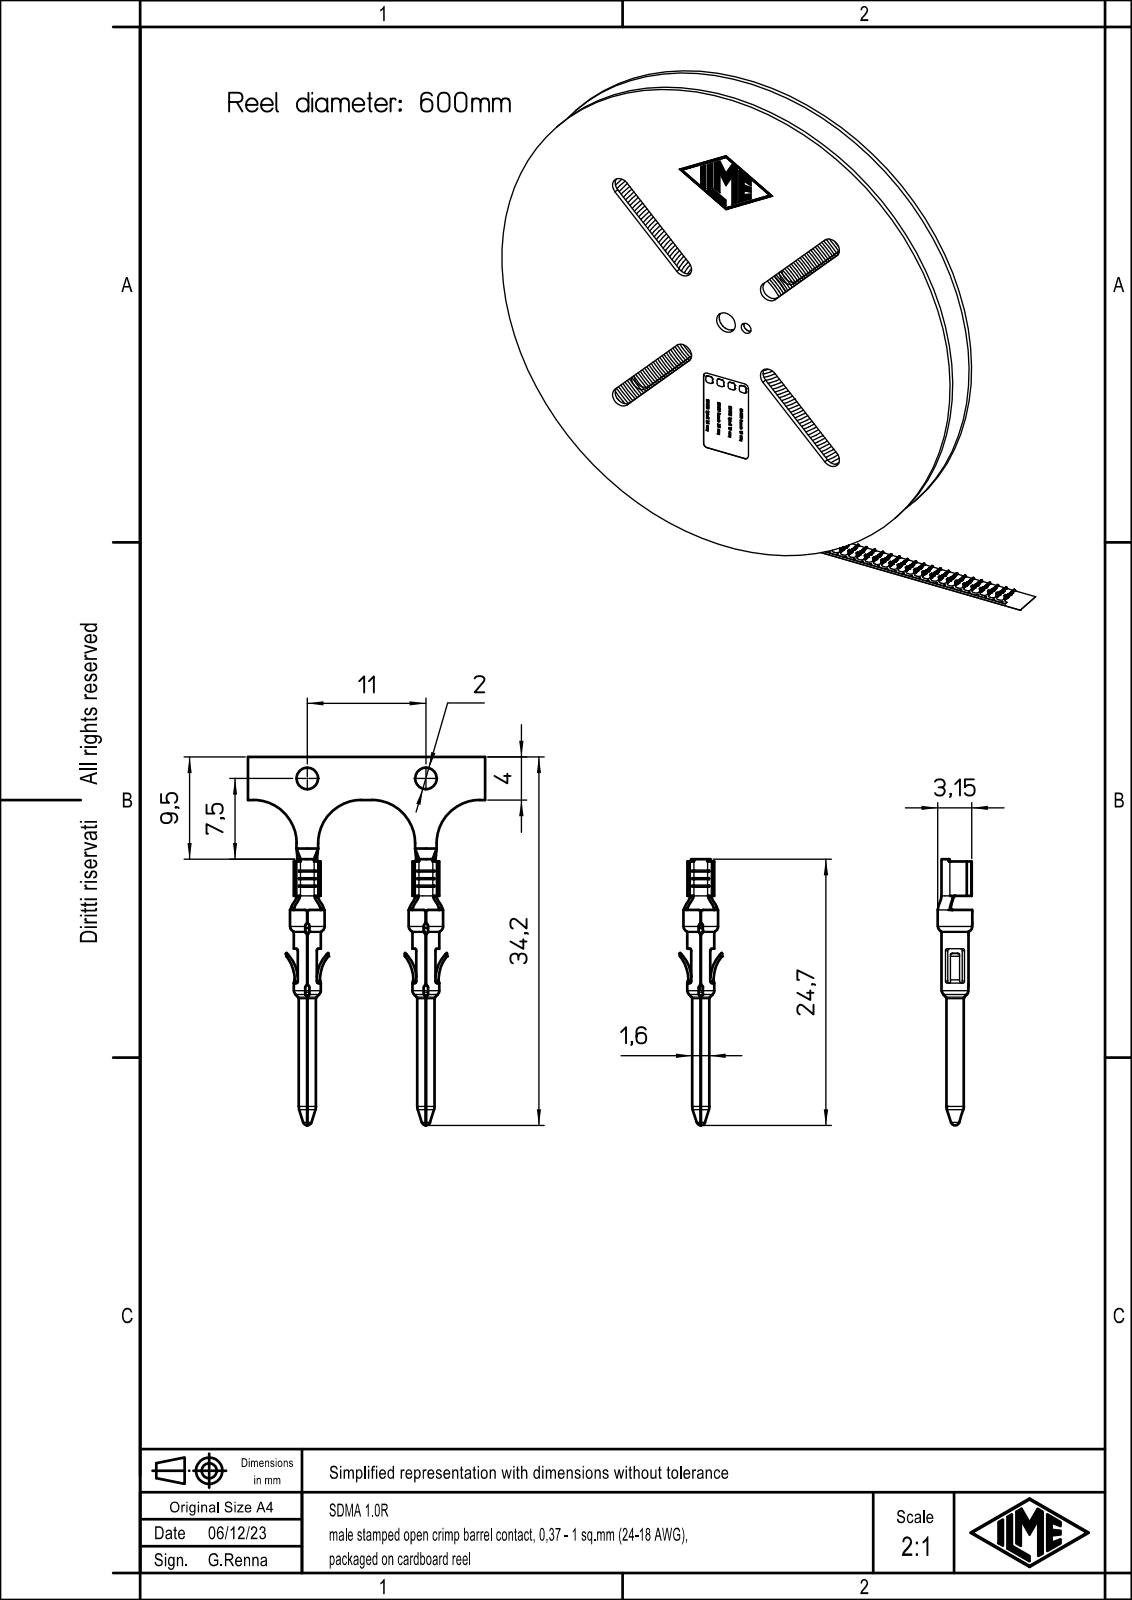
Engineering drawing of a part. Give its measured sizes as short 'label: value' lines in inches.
name: SDMA_1.0
written by: Creo Elements/Direct Modeling 20.1B 02-Apr-2019 (C) Parametric Technology GmbH (AUTOMOTIVE_DESIGN)
unit: in
bodies: 1 solid, 205 faces (66 planar, 91 cylindrical, 48 other)
size: 0.972 × 0.156 × 0.126
volume: 0.002 in³; area: 0.453 in²
holes: 1× ⌀0.039, 1× ⌀0.075, 1× ⌀0.098, 1× ⌀0.102
bosses: 1× ⌀0.126, 1× ⌀0.063
rounds: 32× R0.008, 4× R0.138, 2× R0.004, 1× R0.026, 1× R0.03, 1× R0.037
face distances: 0.033, 0.177, 0.126, 0.051, 0.319, 0.142, 0.193, 0.327, 0.185, 0.134
